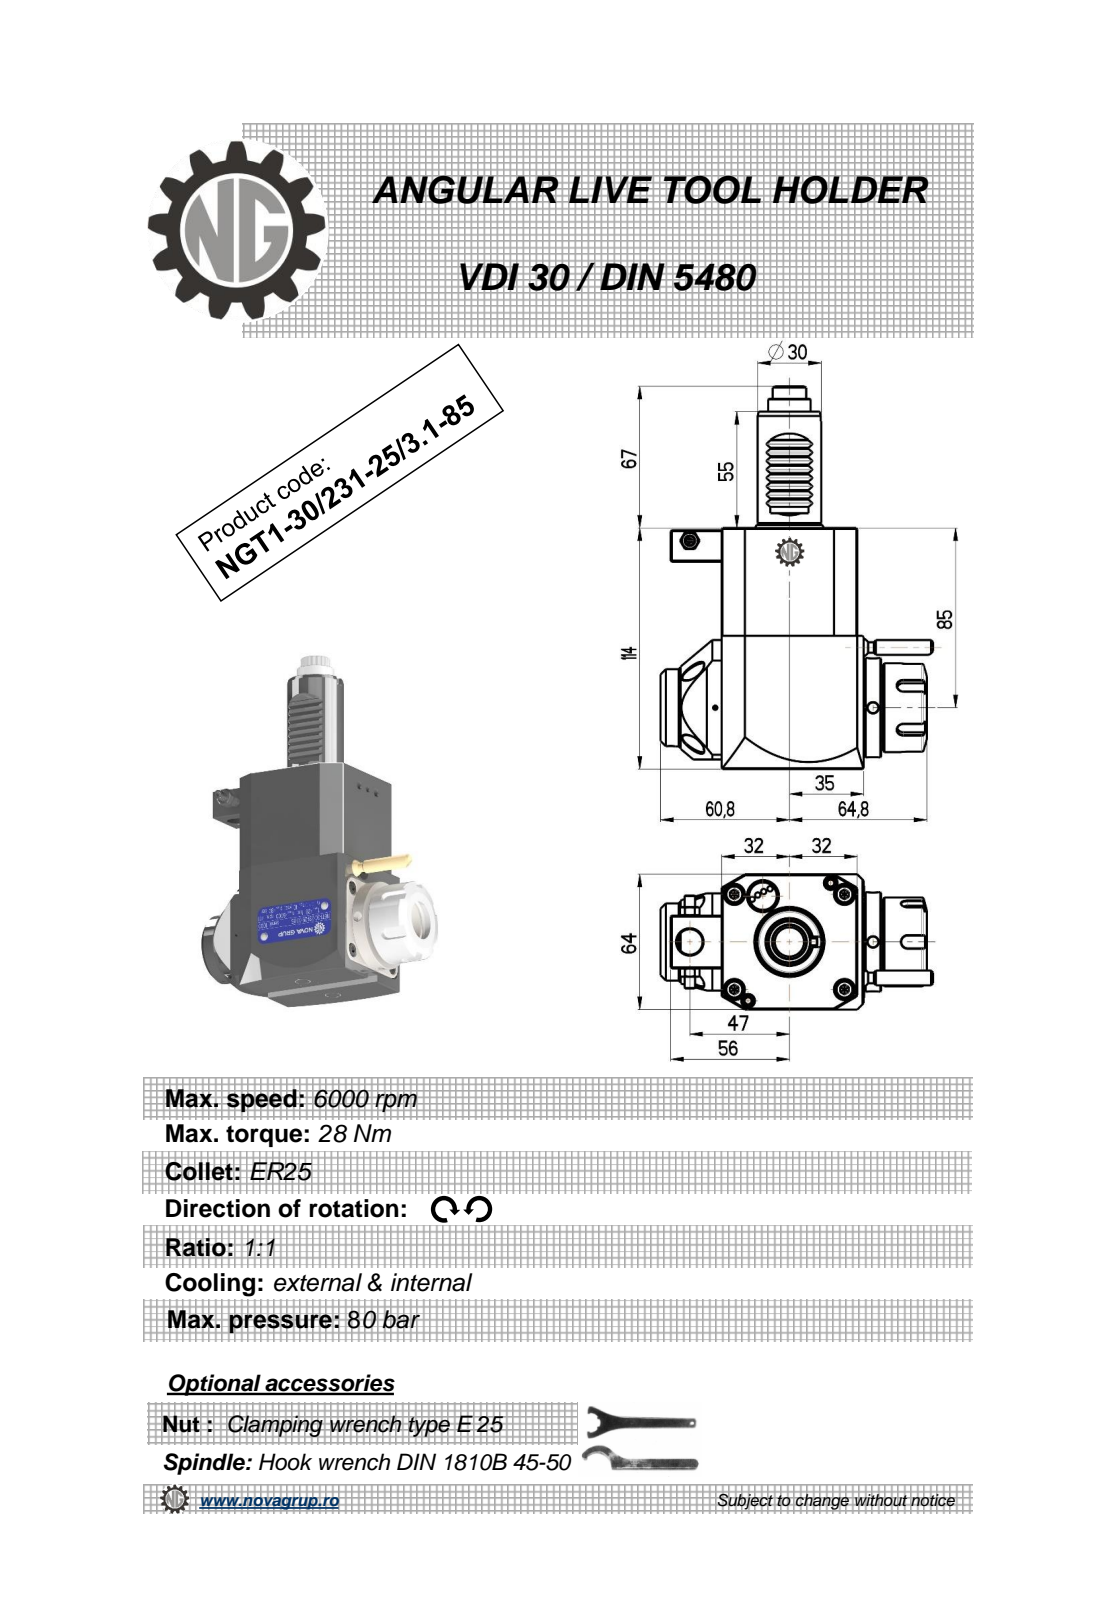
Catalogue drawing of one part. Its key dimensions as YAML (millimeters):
part_name: "NGT1_30_231_25_3_1_85"
step_written_by: "PRO/ENGINEER BY PARAMETRIC TECHNOLOGY CORPORATION, 2010280 (CONFIG_CONTROL_DESIGN)"
units: millimeters
bodies: {solids: 1, faces: 515, planar: 194, cylindrical: 155, other: 166}
overall_size: [181, 128.63, 64]
volume: 599323
surface_area: 56791
round_holes:
  - {diameter: 5, count: 2}
  - {diameter: 2.5, count: 1}
  - {diameter: 3, count: 1}
  - {diameter: 4.2, count: 1}
  - {diameter: 9.5, count: 1}
  - {diameter: 12, count: 1}
  - {diameter: 20.3, count: 1}
round_bosses_or_shafts:
  - {diameter: 8.96, count: 2}
  - {diameter: 5, count: 2}
  - {diameter: 47, count: 1}
  - {diameter: 42, count: 1}
  - {diameter: 36.5, count: 1}
  - {diameter: 35, count: 1}
  - {diameter: 30, count: 1}
  - {diameter: 20, count: 1}
partial_cylinders:
  - {radius: 1.98, count: 36}
  - {radius: 0.26, count: 12}
  - {radius: 0.3, count: 8}
  - {radius: 3, count: 5}
  - {radius: 160, count: 2}
  - {radius: 7.08, count: 1}
  - {radius: 7.92, count: 1}
  - {radius: 13, count: 1}
face_to_face_distances: [64, 114, 0.5, 67, 67.2, 3.2, 76.42, 7.5, 3, 8]
hole_center_spacings: [33.19, 50.92, 76.5, 86.45, 117.11]
